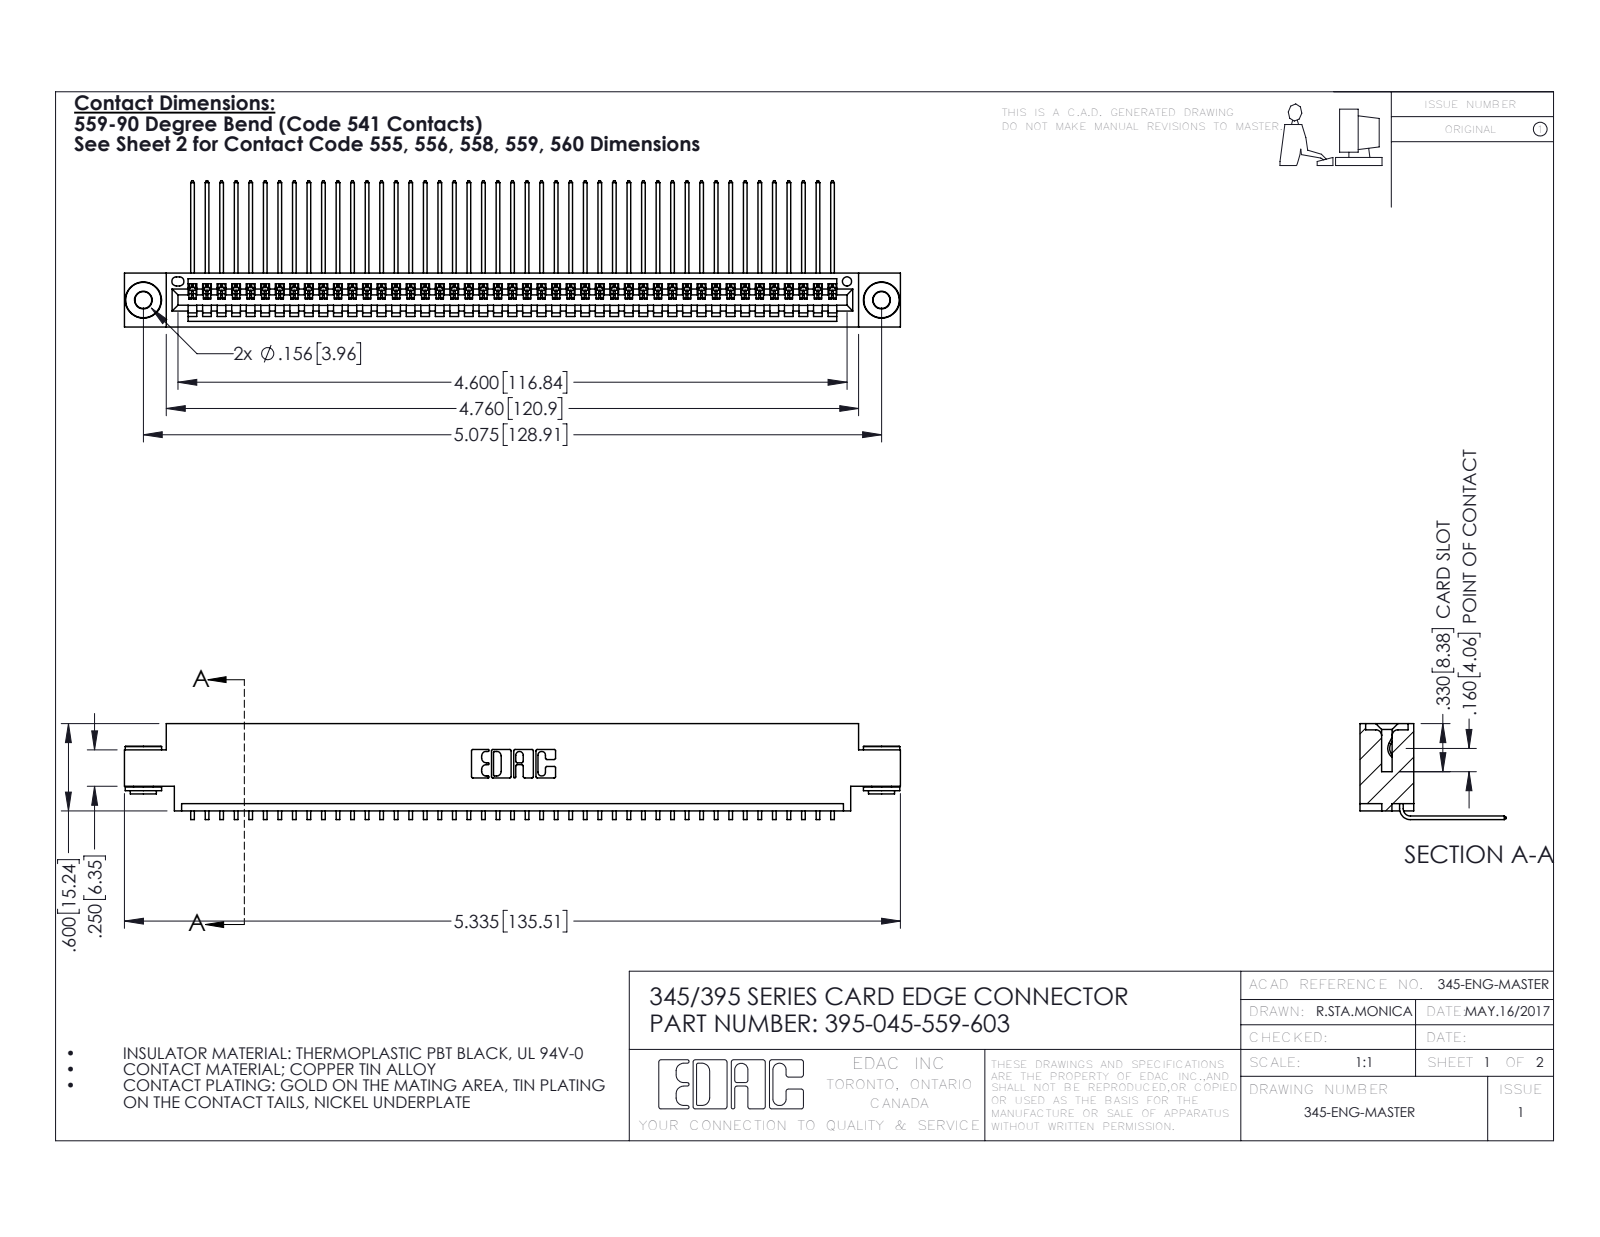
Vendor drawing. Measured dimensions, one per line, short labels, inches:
name: 395-045-559-603; 345 Part_0.170 Offset - 0.156 Dia-TH; 345-250-002_345-250-002-102; 345-292-001_558 559 Tail - 1
written by: SolidWorks 2016 (CONFIG_CONTROL_DESIGN)
unit: in
bodies: 48 solids, 2868 faces (1984 planar, 876 cylindrical, 8 other)
size: 5.335 × 1.005 × 0.659
volume: 0.79 in³; area: 28.63 in²
holes: 2× ⌀0.116, 2× ⌀0.156, 1× ⌀0.064
bosses: 2× ⌀0.25, 2× ⌀0.18, 2× ⌀0.136
rounds: 90× R0.006, 22× R0.01, 6× R0.007, 6× R0.031, 3× R0.026, 2× R0.031, 2× R0.04, 1× R0.014
face distances: 0.072, 0.298, 0.37, 0.2, 0.098, 0.272, 0.025, 0.225, 0.175, 0.149
hole spacings: 0.27, 4.839, 5.075
